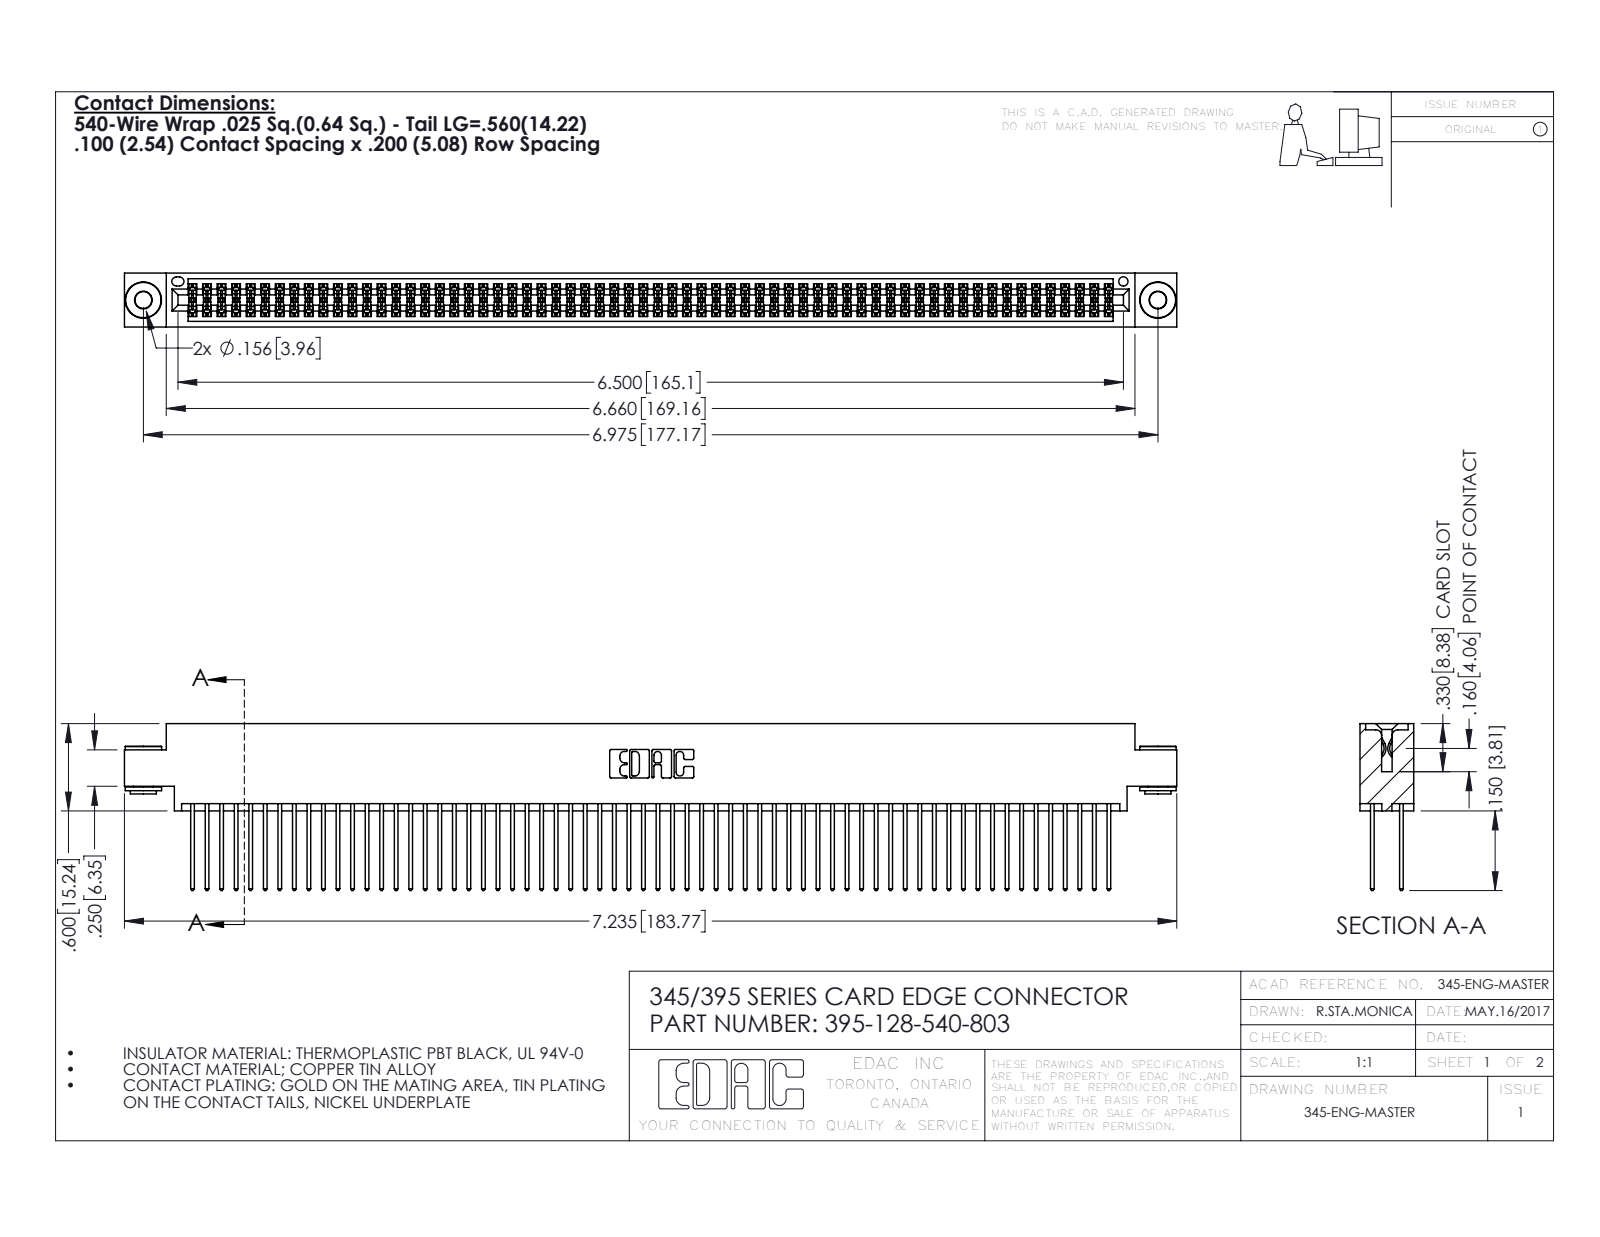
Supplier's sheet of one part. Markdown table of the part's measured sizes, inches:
| quantity | value |
| --- | --- |
| part name | 345-292-001_345-293-140; 345 Part_0.170 Offset - 0.156 Dia-TH; 395-128-540-803; 345-250-002_345-250-002-102 |
| STEP written by | SolidWorks 2016 (CONFIG_CONTROL_DESIGN) |
| units | inches |
| bodies | 131 solids, 6568 faces (4318 planar, 2242 cylindrical, 8 other) |
| overall size | 7.235 × 1.147 × 0.37 |
| volume | 1.126 in³ |
| surface area | 46.95 in² |
| round holes (diameter × count) | 0.116 × 2, 0.156 × 2, 0.064 × 1 |
| round bosses / shafts (diameter × count) | 0.25 × 2, 0.18 × 2, 0.136 × 2 |
| partial cylindrical surfaces (radius × count) | 0.006 × 192, 0.01 × 128, 0.01 × 22, 0.007 × 6, 0.031 × 6, 0.026 × 3, 0.014 × 2, 0.019 × 2 |
| main face-to-face distances | 0.072, 0.298, 0.2, 0.098, 0.272, 0.025, 0.37, 0.225, 0.175, 0.149 |
| hole center spacings | 0.27, 6.739, 6.975 |
